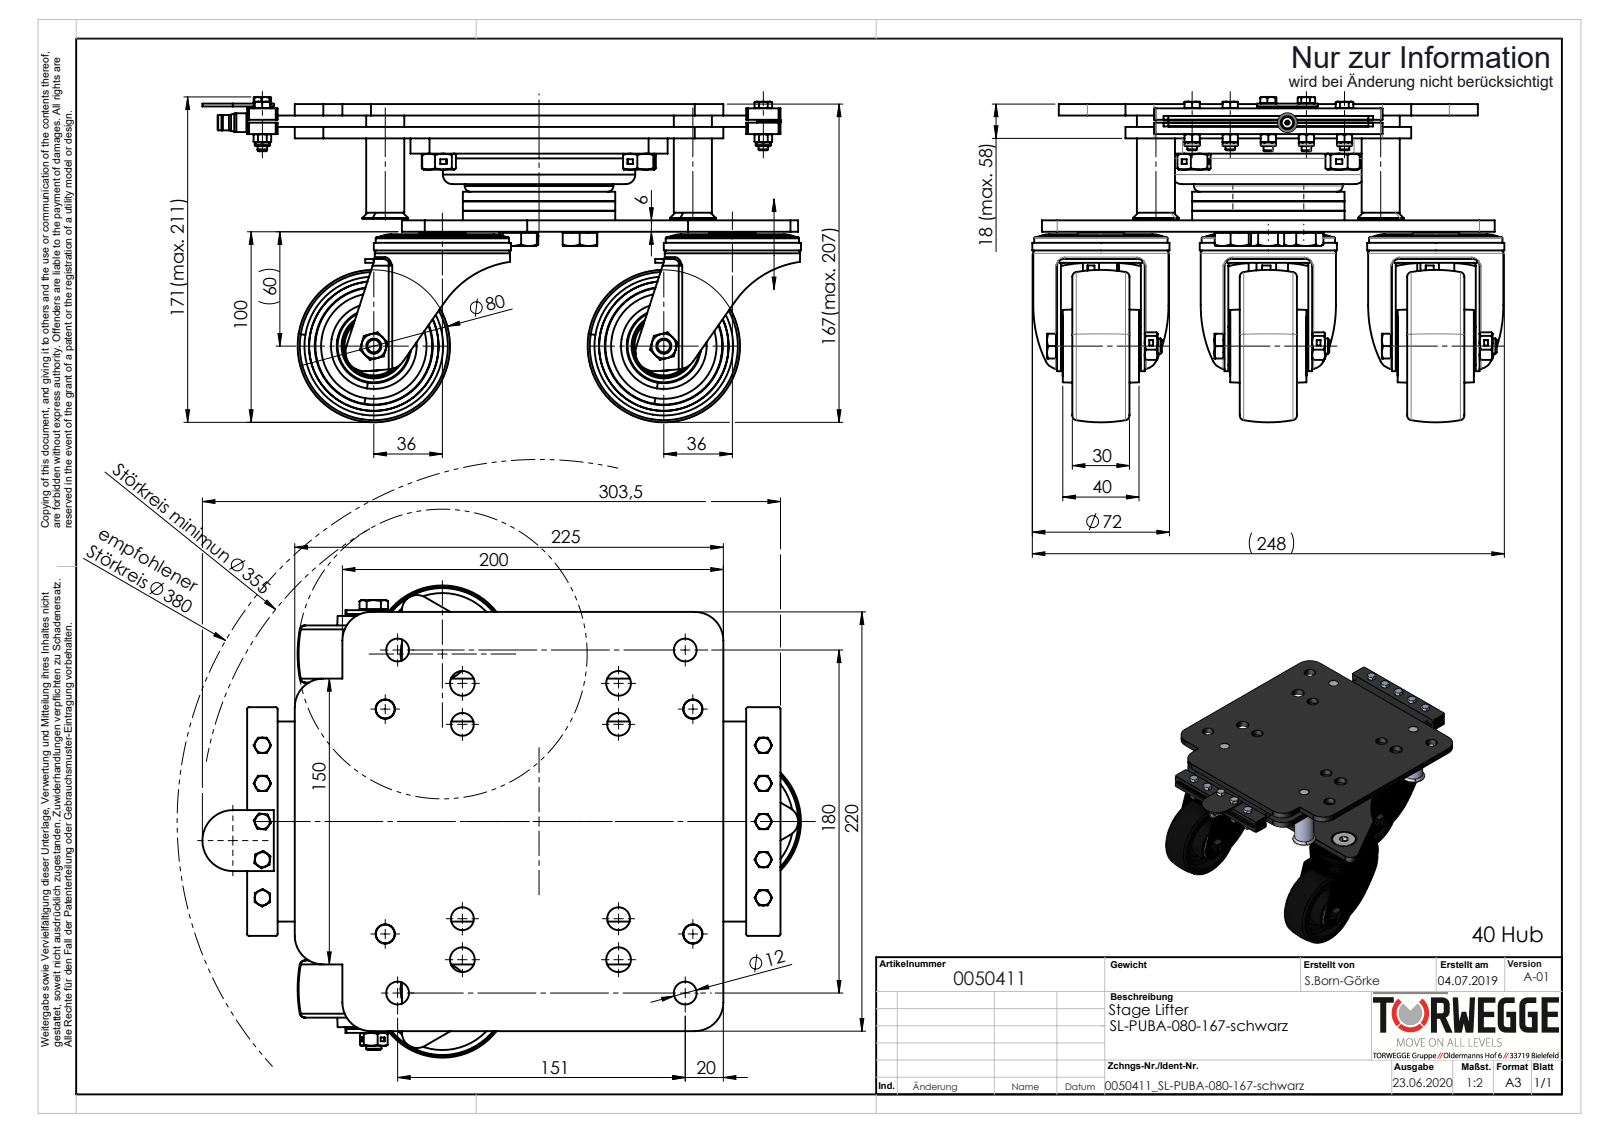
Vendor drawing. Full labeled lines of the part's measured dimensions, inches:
Part name (STEP PRODUCT): 0050411
STEP written by: SolidWorks 2018 (AUTOMOTIVE_DESIGN)
Units: inches
Bodies: 141 solids, 2864 faces (1061 planar, 836 cylindrical, 967 other)
Overall size (bounding box): 12.372 × 9.756 × 6.723
Volume: 106.9 in³ · Surface area: 1 163 in²
Round holes (diameter × count): ⌀0.472 ×19, ⌀0.163 ×10, ⌀0.197 ×10, ⌀0.226 ×10, ⌀0.402 ×10, ⌀0.492 ×7, ⌀0.512 ×7, ⌀0.335 ×4, ⌀0.394 ×4, ⌀0.866 ×4, ⌀0.236 ×3, ⌀0.551 ×3
Round bosses / shafts (diameter × count): ⌀0.202 ×16, ⌀0.787 ×10, ⌀0.315 ×10, ⌀0.945 ×7, ⌀0.709 ×5, ⌀0.472 ×5, ⌀0.387 ×4, ⌀2.835 ×3
Partial cylindrical surfaces — rounded edges, fillets, slot ends (radius × count): R0.591 ×9, R0.039 ×8, R0.098 ×8, R0.217 ×8, R0.394 ×8, R0.059 ×6, R0.138 ×6, R0.177 ×6
Main face-to-face distances: 0.236, 0.472, 2.165, 1.929, 2.402, 0.709, 1.693, 0.197, 2.638, 0.079
Hole centre spacings: 4.48, 0.846, 1.363, 3.15, 3.228, 3.337, 4.015, 4.862
